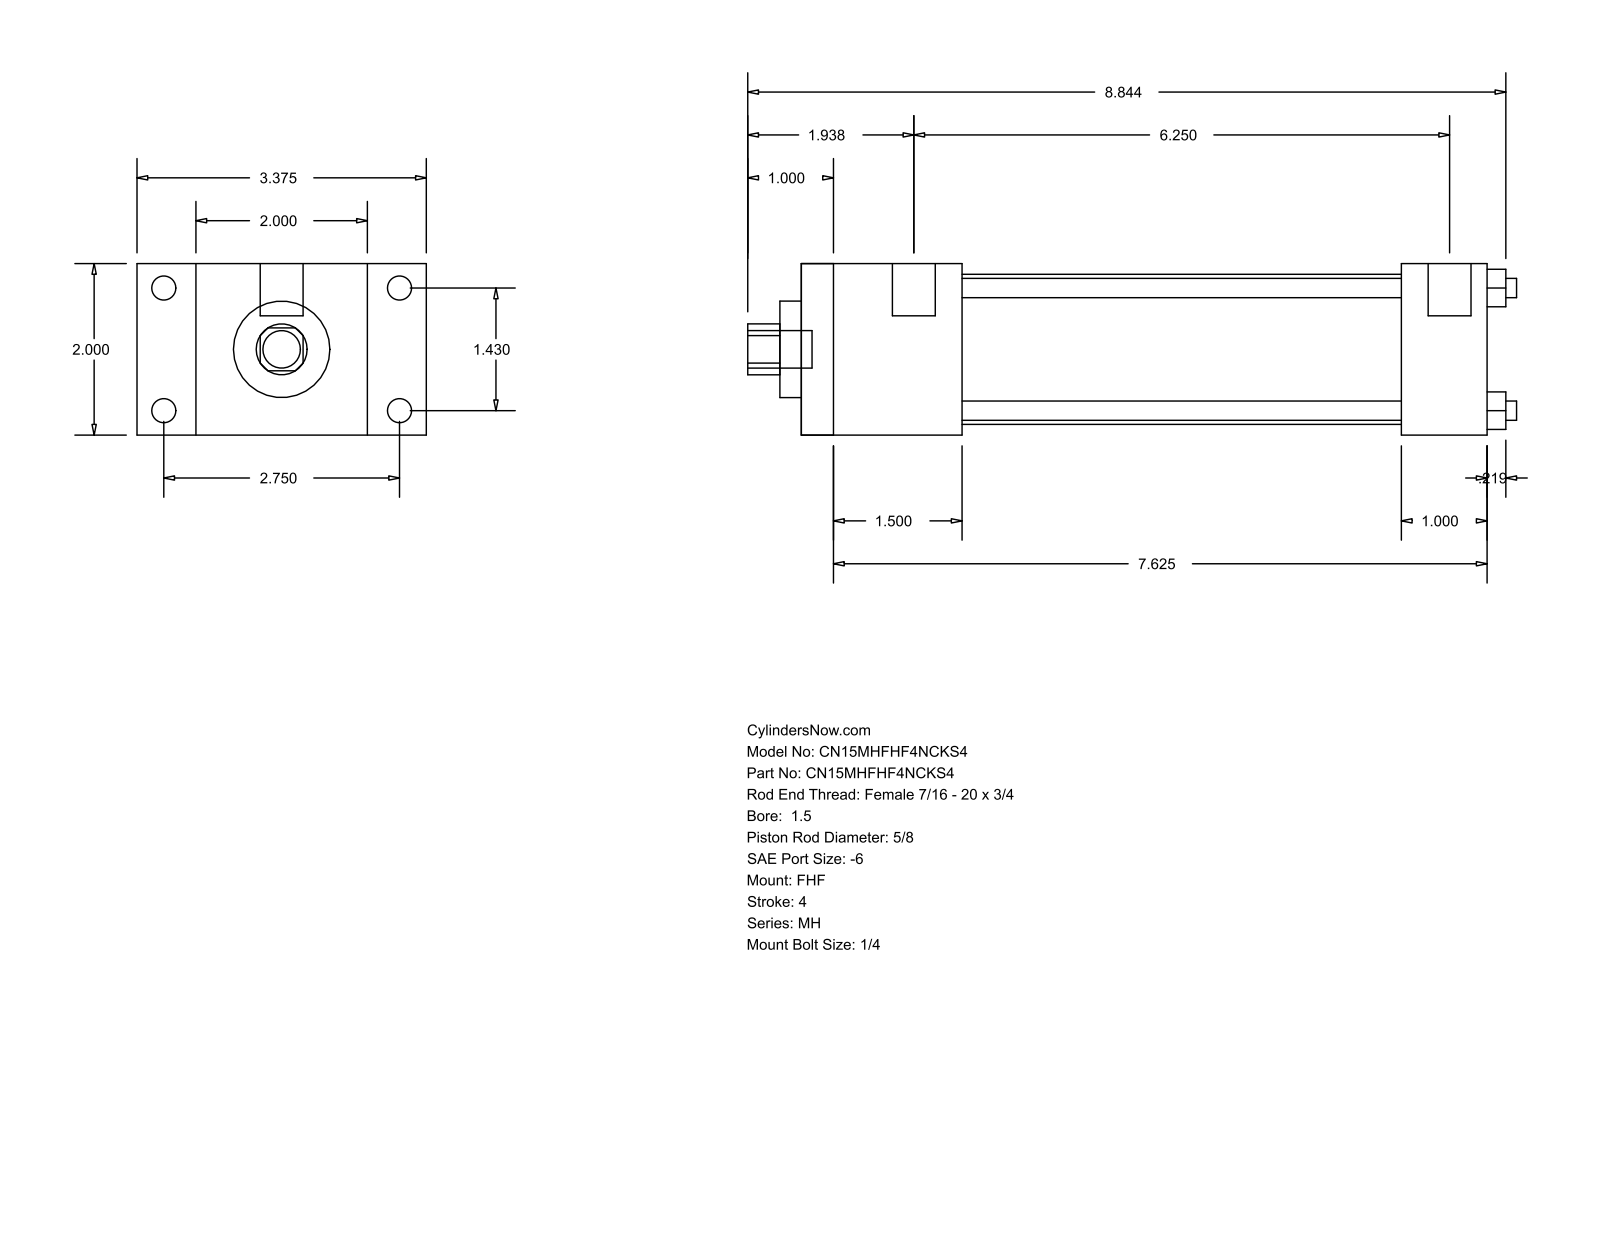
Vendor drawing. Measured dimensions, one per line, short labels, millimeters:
name: MH_FHF__0150_0.625
written by: GSSL Pune (CONFIG_CONTROL_DESIGN)
unit: mm
bodies: 0 solids, 88 faces (60 planar, 28 cylindrical, 0 other)
size: 227.81 × 85.72 × 50.8
holes: 4× ⌀5.71, 1× ⌀15.88, 1× ⌀28.57, 1× ⌀44.45
bosses: 4× ⌀7.14, 4× ⌀5.56, 2× ⌀12.7, 1× ⌀11.11
rounds: 1× R7.54
face distances: 50.8, 17.46, 68.26, 47.62, 85.72, 203.19, 155.57, 177.8, 130.18, 25.39
hole spacings: 25.68, 36.32, 51.36
